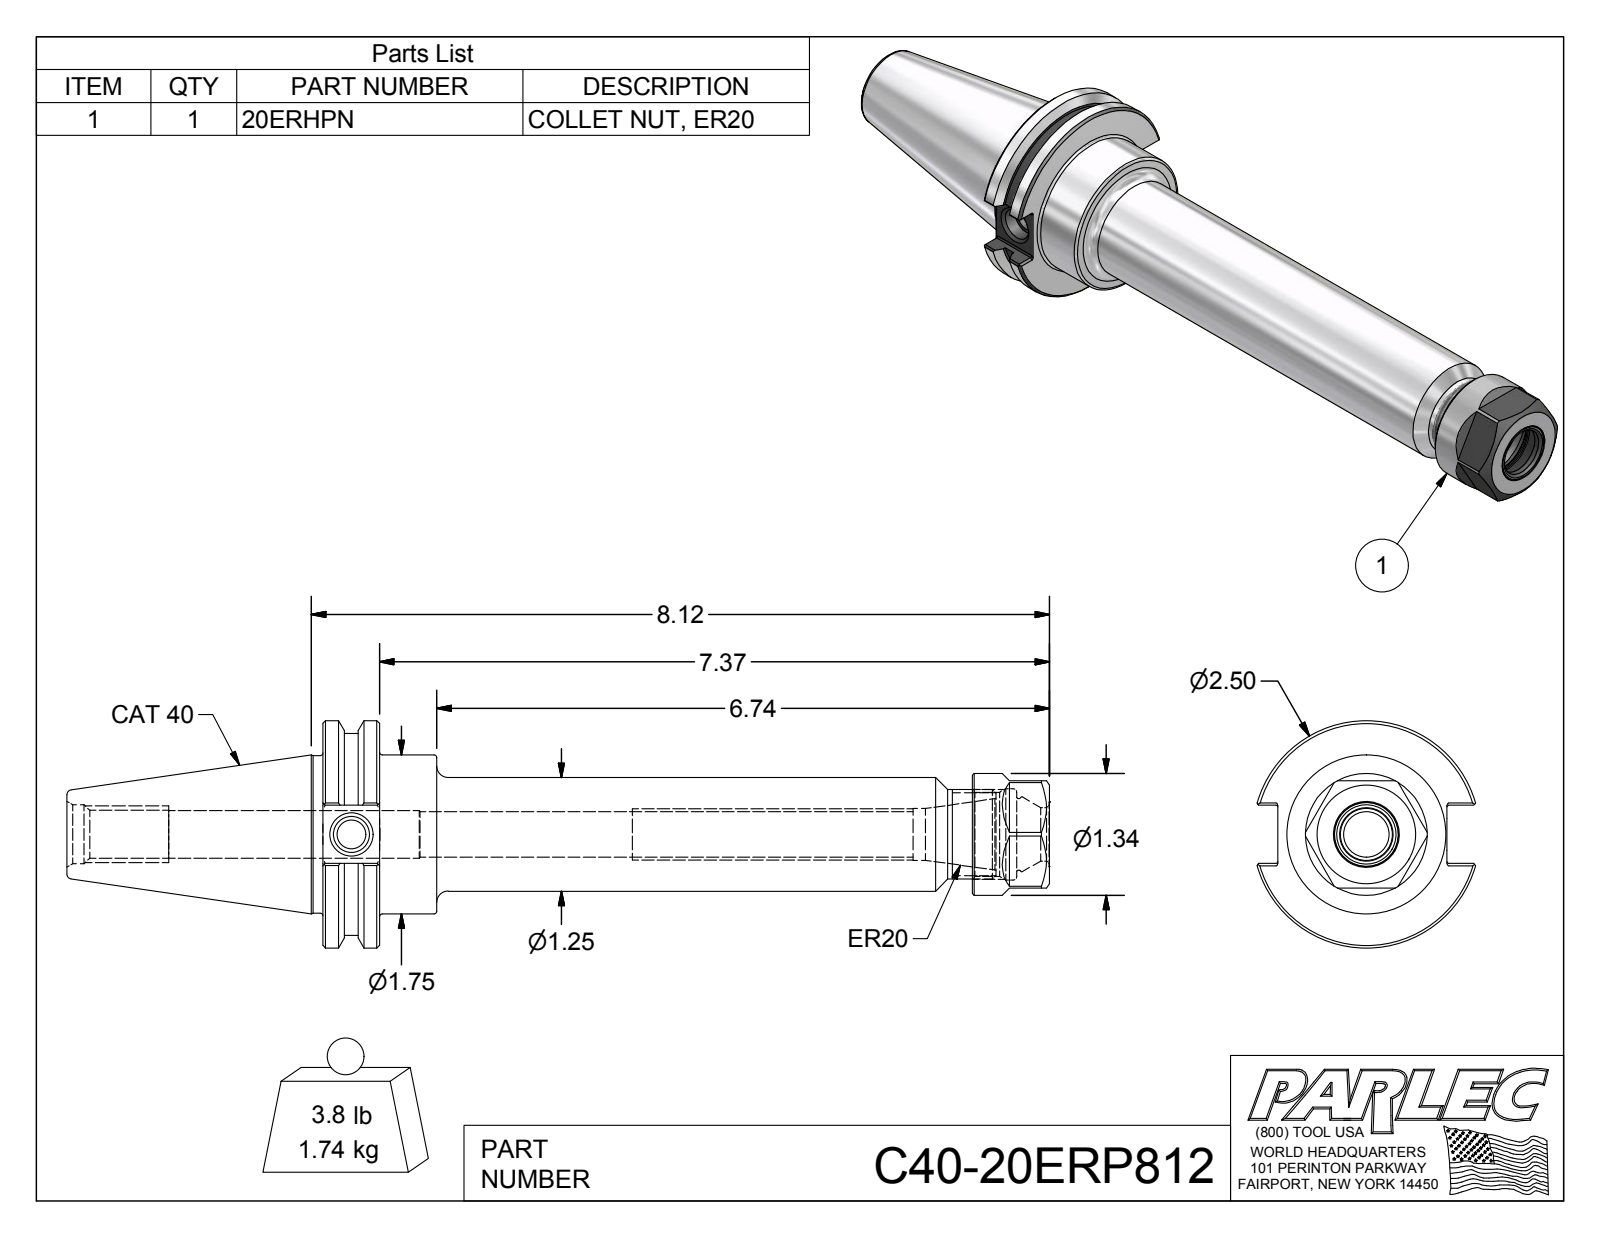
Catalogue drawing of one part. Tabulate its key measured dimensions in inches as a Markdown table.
| quantity | value |
| --- | --- |
| part name | C40-20ERP812; C40-20ER8-1; 20ERHPN |
| STEP written by | Autodesk Inventor 2012 (AUTOMOTIVE_DESIGN) |
| units | inches |
| bodies | 2 solids, 120 faces (49 planar, 34 cylindrical, 37 other) |
| overall size | 10.808 × 2.5 × 2.403 |
| volume | 14.04 in³ |
| surface area | 76.29 in² |
| round holes (diameter × count) | 0.315 × 1, 0.399 × 1, 0.502 × 1, 0.526 × 1, 0.527 × 1, 0.57 × 1, 0.587 × 1, 0.648 × 1, 0.79 × 1, 0.926 × 1, 1.005 × 1 |
| round bosses / shafts (diameter × count) | 2.5 × 1, 2.219 × 1, 1.75 × 1, 1.73 × 1, 1.34 × 1, 1.25 × 1, 0.984 × 1 |
| partial cylindrical surfaces (radius × count) | 0.02 × 12 |
| main face-to-face distances | 0.625, 1.18, 7.145, 6.52, 7.995, 7.37, 0.85, 1.255, 0.63, 5.89 |
